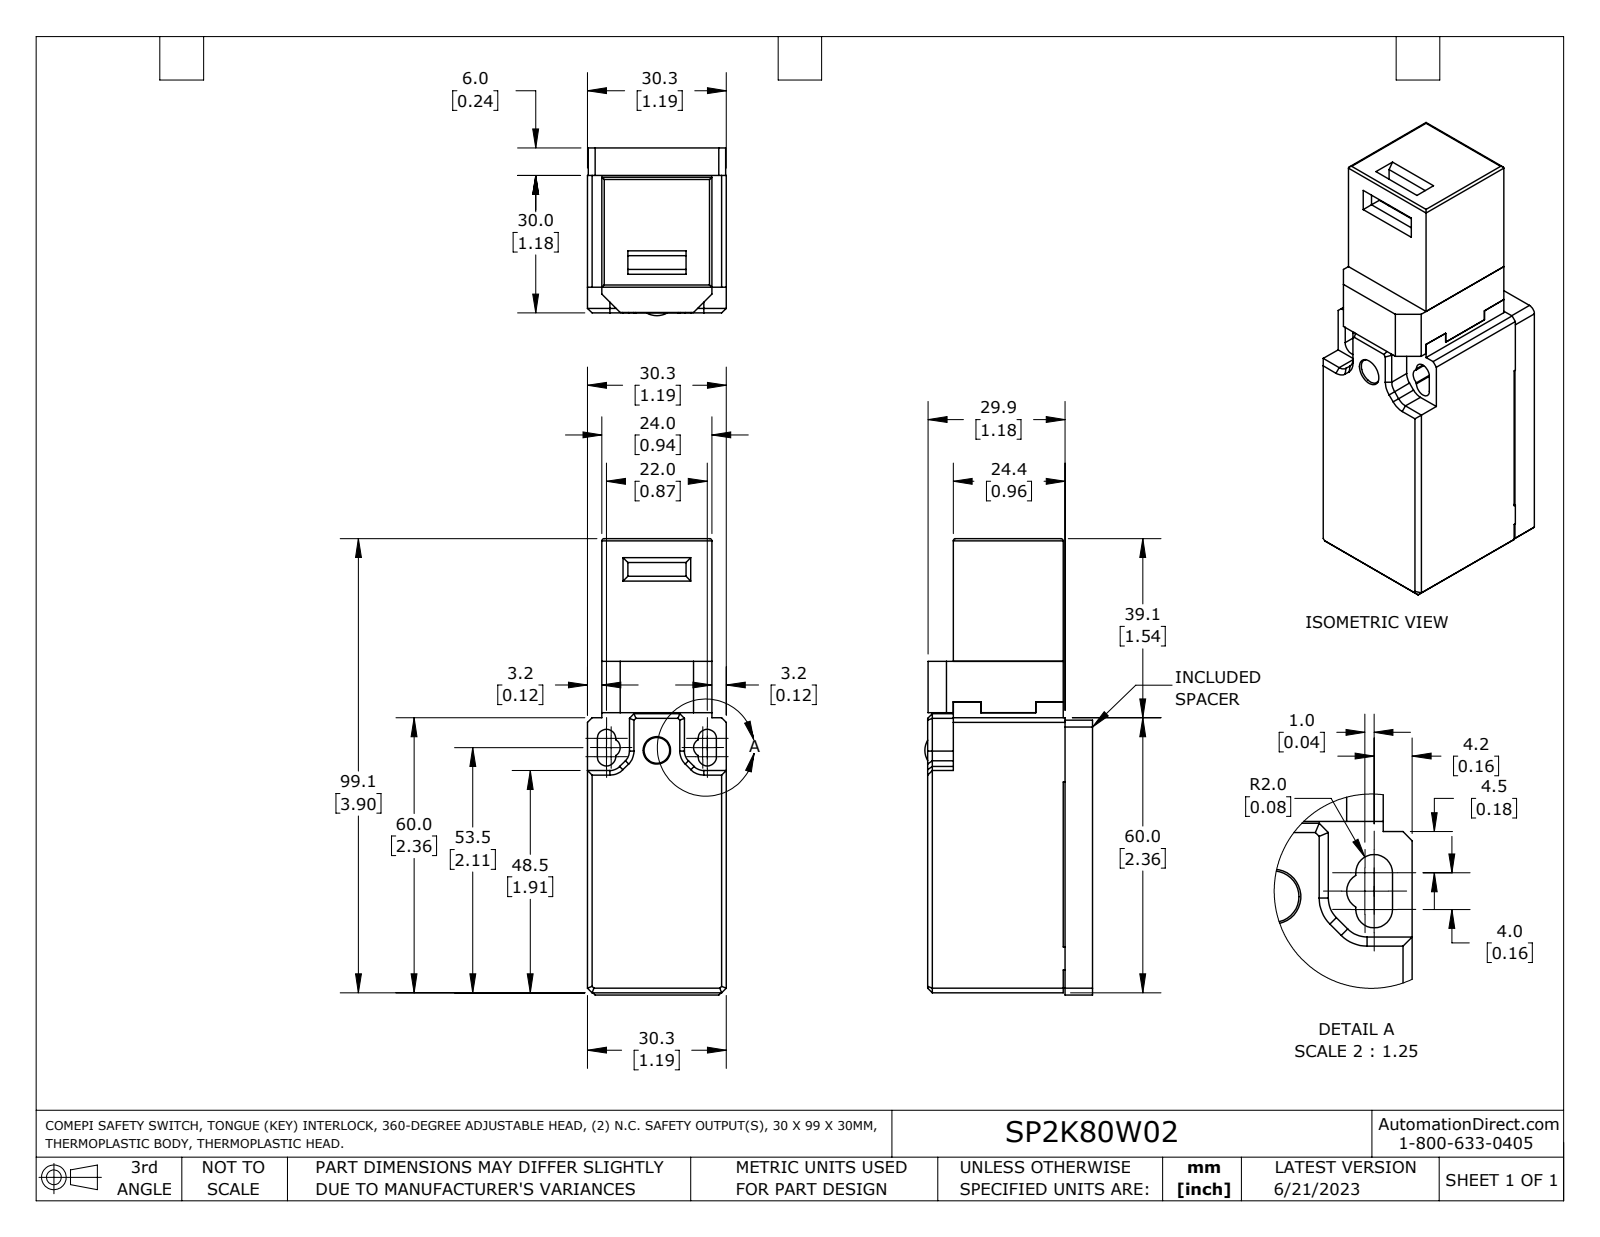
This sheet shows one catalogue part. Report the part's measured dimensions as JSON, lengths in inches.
{"part_name": "SP2K80W02", "step_written_by": "SolidWorks 2021 (AUTOMOTIVE_DESIGN)", "units": "inches", "bodies": {"solids": 4, "faces": 262, "planar": 173, "cylindrical": 80, "other": 9}, "overall_size": [3.921, 1.441, 1.193], "volume_in3": 4.652, "surface_area_in2": 36.23, "round_holes": [[0.236, 1], [0.591, 1], [0.669, 1], [0.748, 1]], "round_bosses_or_shafts": [[0.22, 1]], "partial_cylinders_radius": [[0.079, 30], [0.016, 24], [0.02, 4], [0.118, 4], [0.059, 2], [0.091, 2], [0.394, 1], [0.4, 1]], "face_to_face_distances": [0.124, 1.069, 0.945, 1.193, 1.181, 1.165, 0.236, 0.016, 1.197, 0.079], "hole_center_spacings": [0.083]}
